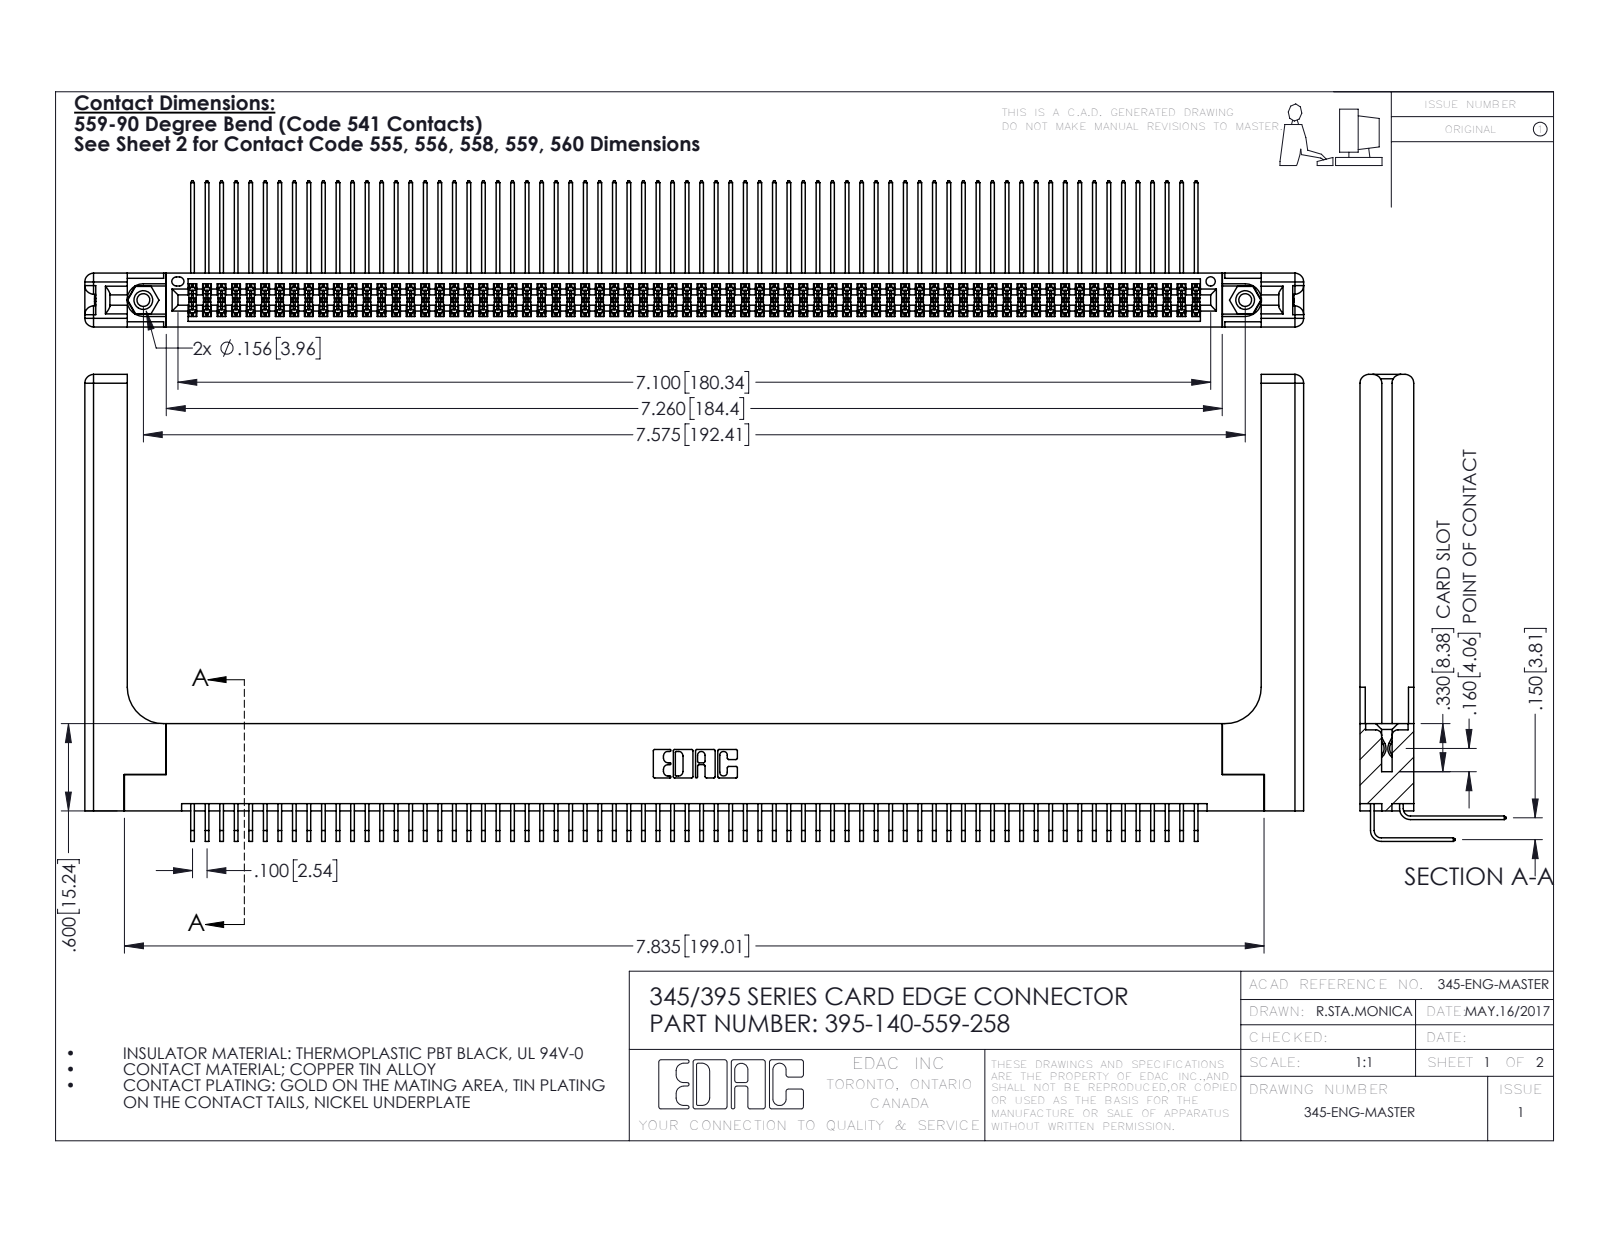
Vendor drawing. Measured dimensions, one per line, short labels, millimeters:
name: 345-292-001_559 Tail - 2; 345-220-058_345-220-058; 395-140-559-258; 345-292-001_558 559 Tail - 1 (+2 more)
written by: SolidWorks 2016 (CONFIG_CONTROL_DESIGN)
unit: mm
bodies: 145 solids, 7662 faces (5128 planar, 2474 cylindrical, 60 other)
size: 212.8 × 81.5 × 25.5
volume: 30 220 mm³; area: 41 540 mm²
holes: 2× ⌀2.3, 2× ⌀3.2, 2× ⌀4, 1× ⌀1.6
bosses: 2× ⌀3.9
rounds: 279× R0.2, 22× R0.3, 16× R1.5, 6× R0.2, 6× R0.8, 3× R0.7, 2× R0.4, 2× R0.5
face distances: 1.8, 7.6, 9.4, 5.1, 2.5, 6.9, 0.6, 5.7, 4.4, 3.8
hole spacings: 6.9, 186.4, 192.4
